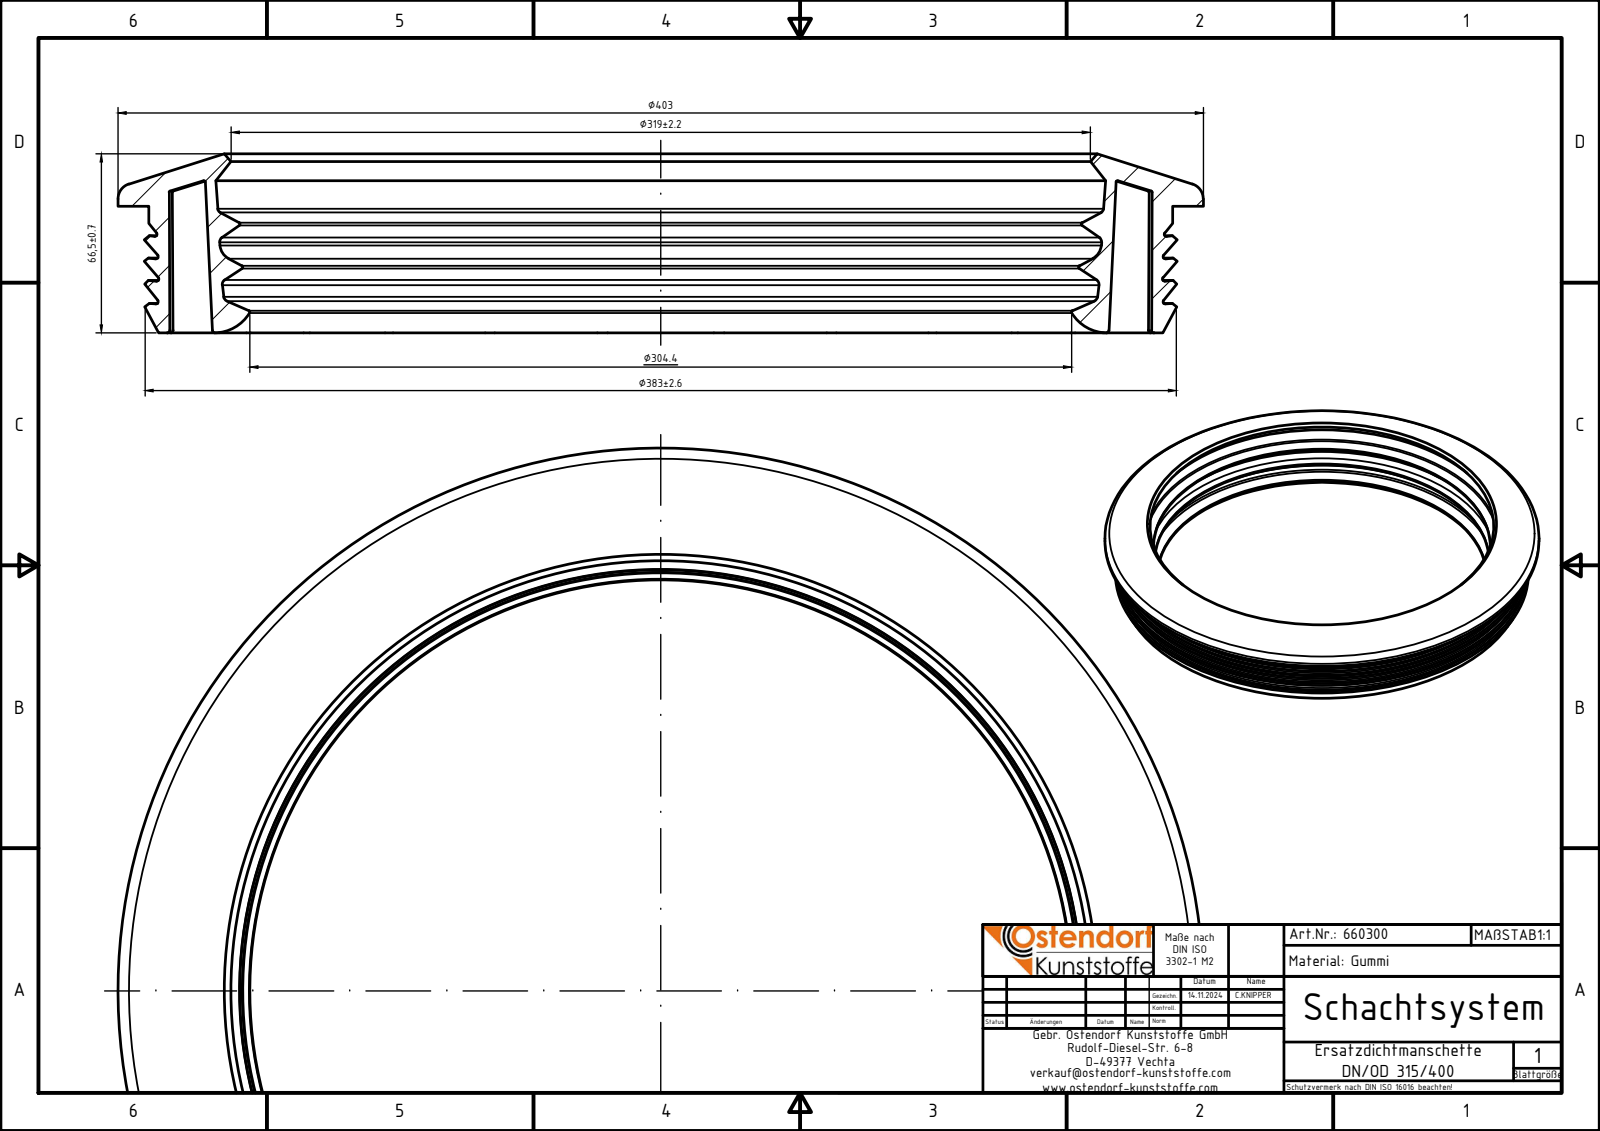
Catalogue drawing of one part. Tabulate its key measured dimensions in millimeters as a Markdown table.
| quantity | value |
| --- | --- |
| part name | 660300z |
| STEP written by | Autodesk Inventor 2024 (AUTOMOTIVE_DESIGN) |
| units | millimeters |
| bodies | 1 solid, 306 faces (50 planar, 50 cylindrical, 206 other) |
| overall size | 403 × 403 × 66.5 |
| volume | 1 306 000 mm³ |
| surface area | 417 109 mm² |
| round bosses / shafts (diameter × count) | 403 × 1, 380.1 × 1 |
| partial cylindrical surfaces (radius × count) | 1 × 48 |
| main face-to-face distances | 47 |
